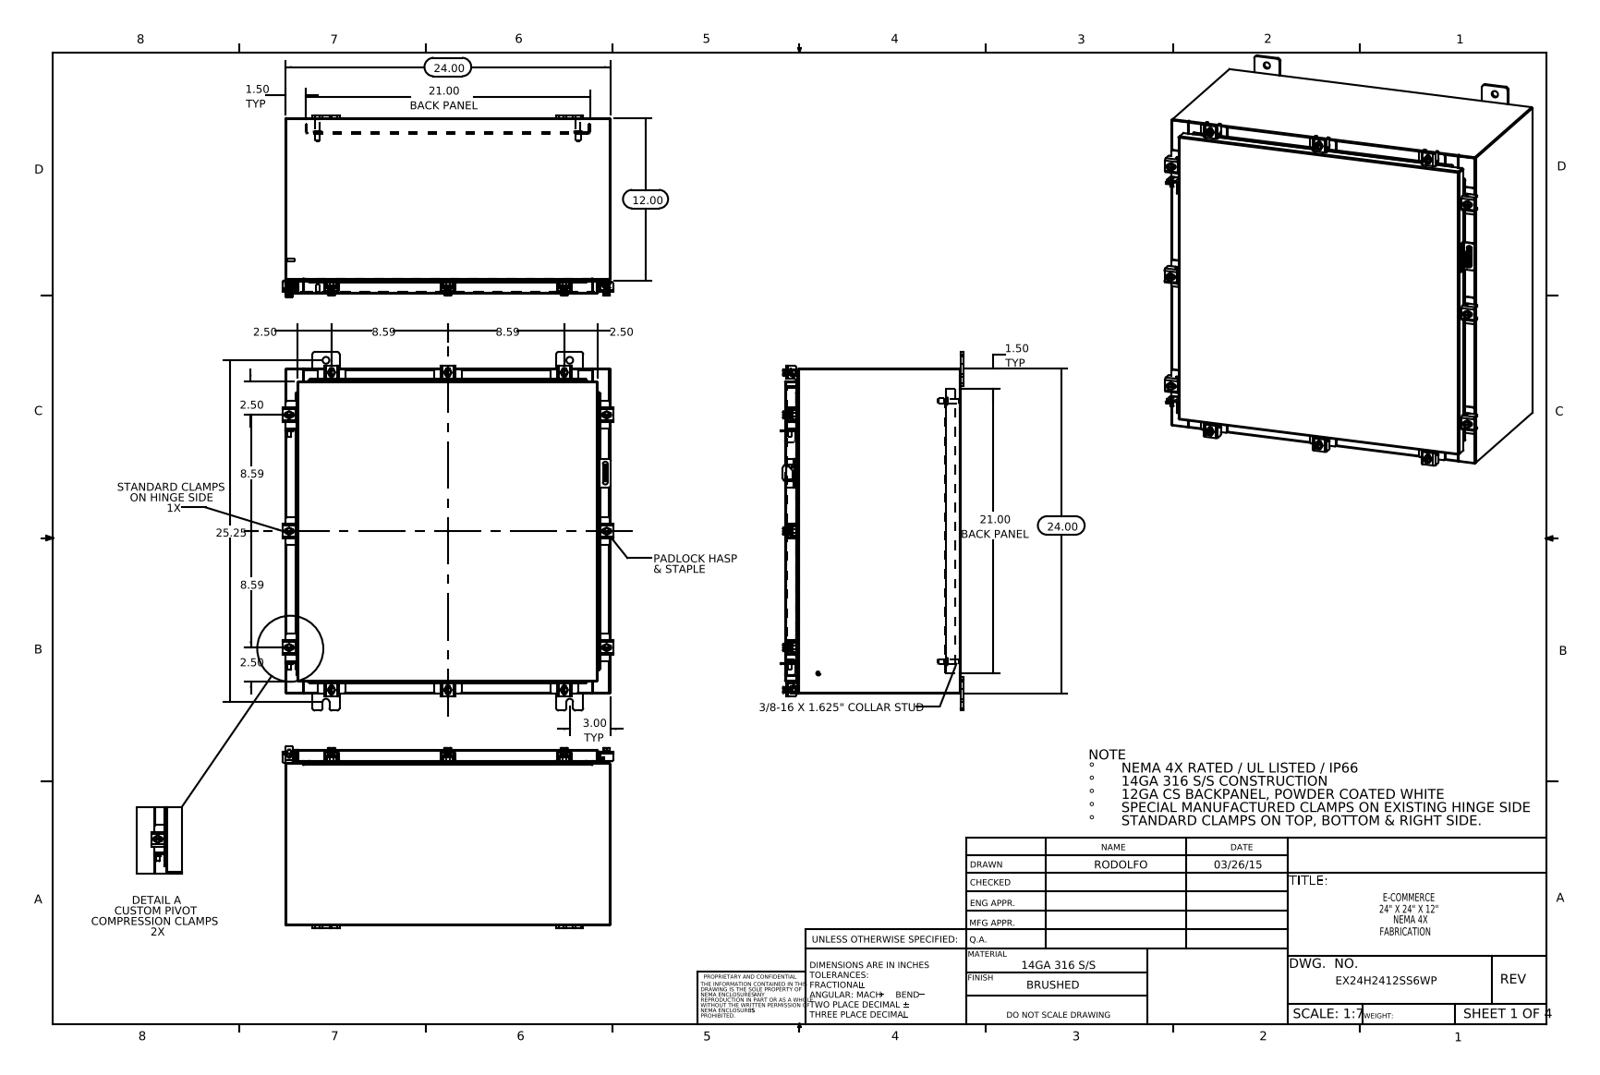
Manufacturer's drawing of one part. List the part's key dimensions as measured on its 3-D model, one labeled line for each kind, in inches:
Part name (STEP PRODUCT): EX24H2412SS6WP Padlock Staple; Clamp Top_RTP31; EX24H2412SS6WP Clamp Assembly; EX24H2412SS6WP (+8 more)
STEP written by: SolidWorks 2014 (CONFIG_CONTROL_DESIGN)
Units: inches
Bodies: 81 solids, 2018 faces (1075 planar, 783 cylindrical, 160 other)
Overall size (bounding box): 26.5 × 24.421 × 13.453
Volume: 245 in³ · Surface area: 6 171 in²
Round holes (diameter × count): ⌀0.213 ×12, ⌀0.26 ×12, ⌀0.5 ×8, ⌀0.125 ×1, ⌀0.25 ×1
Round bosses / shafts (diameter × count): ⌀0.5 ×12, ⌀0.25 ×12, ⌀0.399 ×10, ⌀0.625 ×4, ⌀0.375 ×4, ⌀0.33 ×4, ⌀0.315 ×2, ⌀0.236 ×2
Partial cylindrical surfaces — rounded edges, fillets, slot ends (radius × count): R0.06 ×54, R0.013 ×24, R0.141 ×24, R0.19 ×24, R0.088 ×22, R0.12 ×22, R0.09 ×18, R0.05 ×17
Main face-to-face distances: 0.075, 23.925, 12.9, 23.85, 24, 12.975, 12.826, 0.104, 1, 1.075
Hole centre spacings: 20.559, 2.34, 18.34, 21.376, 23.451, 4.429, 8.593, 8.595
